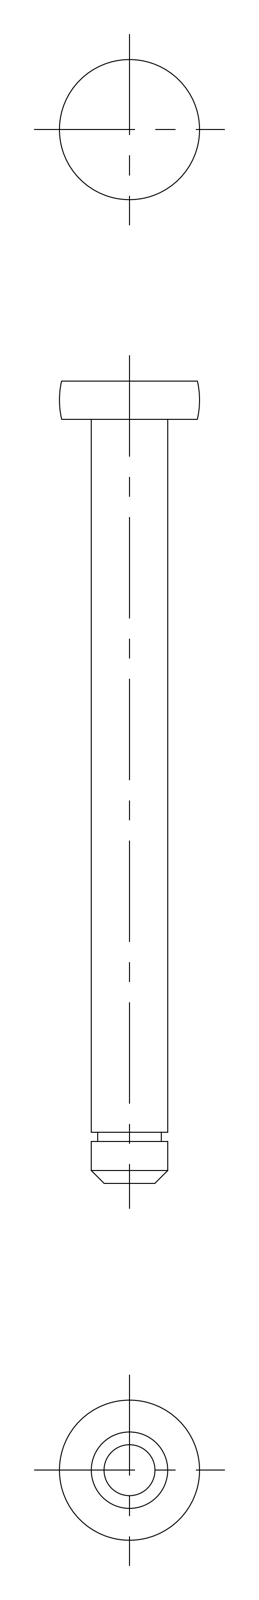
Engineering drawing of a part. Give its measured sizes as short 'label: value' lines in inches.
name: shaft; TH_121_6_60
written by: SolidWorks 2015 (AUTOMOTIVE_DESIGN)
unit: in
bodies: 1 solid, 15 faces (5 planar, 6 cylindrical, 4 other)
size: 2.48 × 0.433 × 0.433
volume: 0.12 in³; area: 2.195 in²
bosses: 1× ⌀0.236, 1× ⌀0.197
face distances: 0.118, 2.362, 2.48, 0.157, 2.205, 2.323, 0.13, 0.028, 2.232, 2.35
